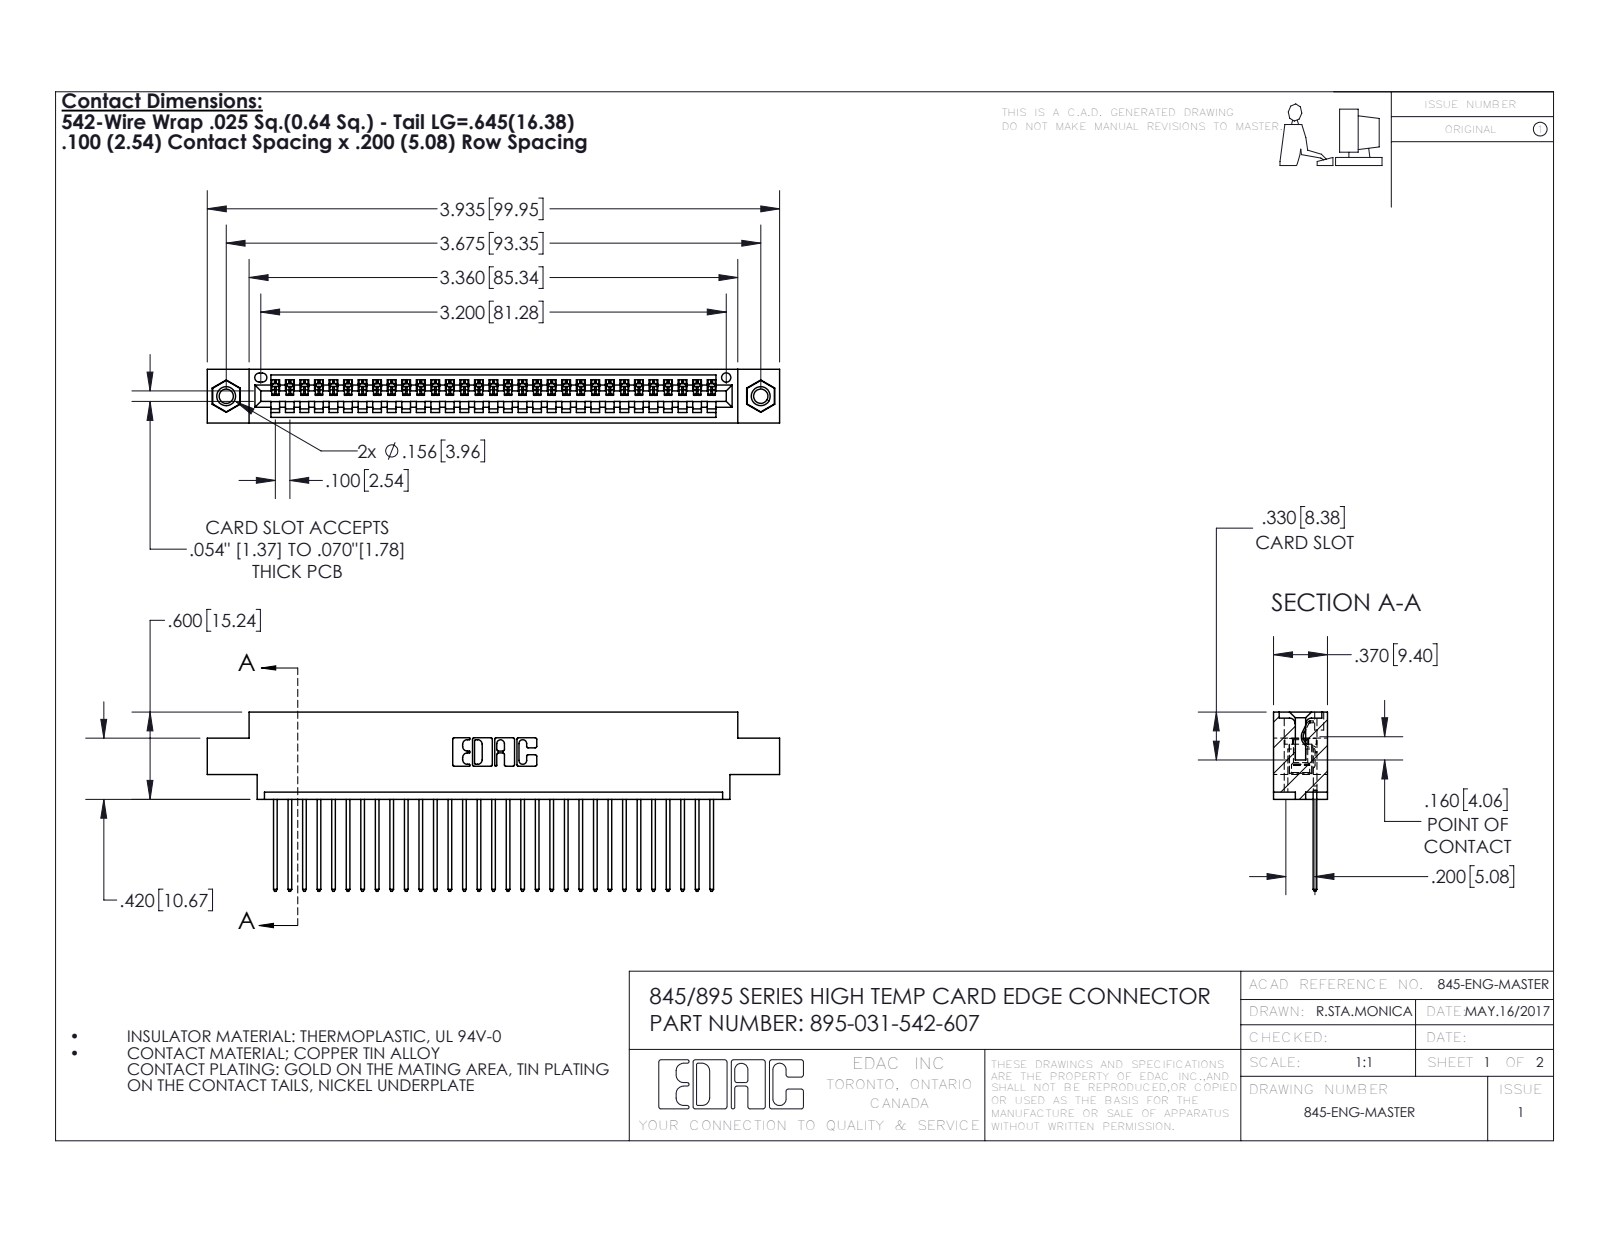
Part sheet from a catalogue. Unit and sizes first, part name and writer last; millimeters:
Units: millimetres
Overall size (bounding box): 99.9 × 31.3 × 9.4
Round holes (diameter × count): ⌀2.5 ×2, ⌀3.2 ×2, ⌀4 ×2, ⌀1.6 ×1
Round bosses / shafts (diameter × count): ⌀3.9 ×2
Partial cylindrical surfaces — rounded edges, fillets, slot ends (radius × count): R0.2 ×62, R0.3 ×62, R0.3 ×22, R0.2 ×6, R0.8 ×6, R0.7 ×3, R0.8 ×2, R1 ×2
Main face-to-face distances: 1.8, 7.6, 9.4, 2.5, 6.9, 0.6, 5.1, 5.7, 4.4, 3.8
Hole centre spacings: 6.9, 87.4, 93.3
Volume: 9 340 mm³ · Surface area: 12 860 mm²
Bodies: 34 solids, 1988 faces (1356 planar, 616 cylindrical, 16 other)
Part name (STEP PRODUCT): 345-292-001_345-293-142; 395-031-542-607; 345 Part_0.170 Offset - 0.156 Dia-TI; 345-250-001_345-250-005-103
STEP written by: SolidWorks 2016 (CONFIG_CONTROL_DESIGN)
